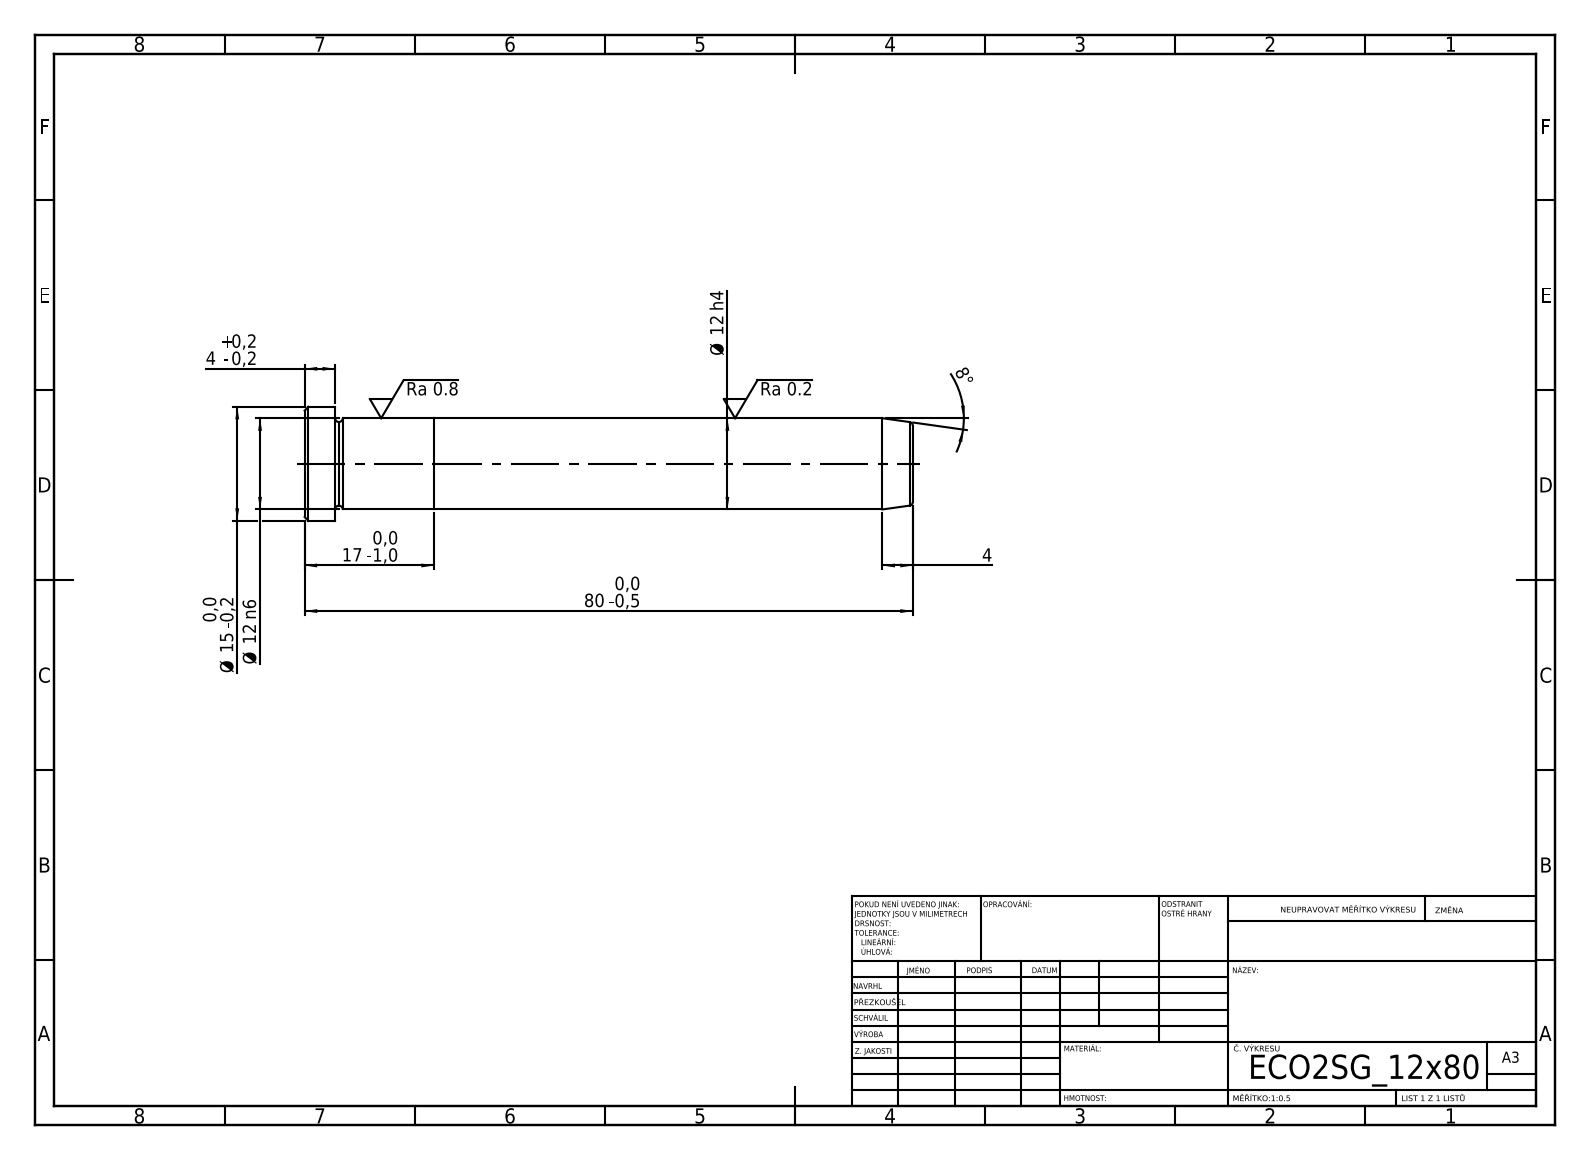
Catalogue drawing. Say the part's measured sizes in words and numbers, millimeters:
Its 3-D file was written by "SolidWorks 2019 (CONFIG_CONTROL_DESIGN)". It is 2 solids with 21 faces: 5 planar, 6 cylindrical and 10 other. Overall it measures 80 by 15 by 15 millimeters. Its volume is 9 240 cubic millimeters and its surface area 3 606 square millimeters. Round bosses or shafts: 1 of diameter 15, 1 of diameter 12. The main face-to-face distances are 17, 63, 80, 76, 13, 4.
